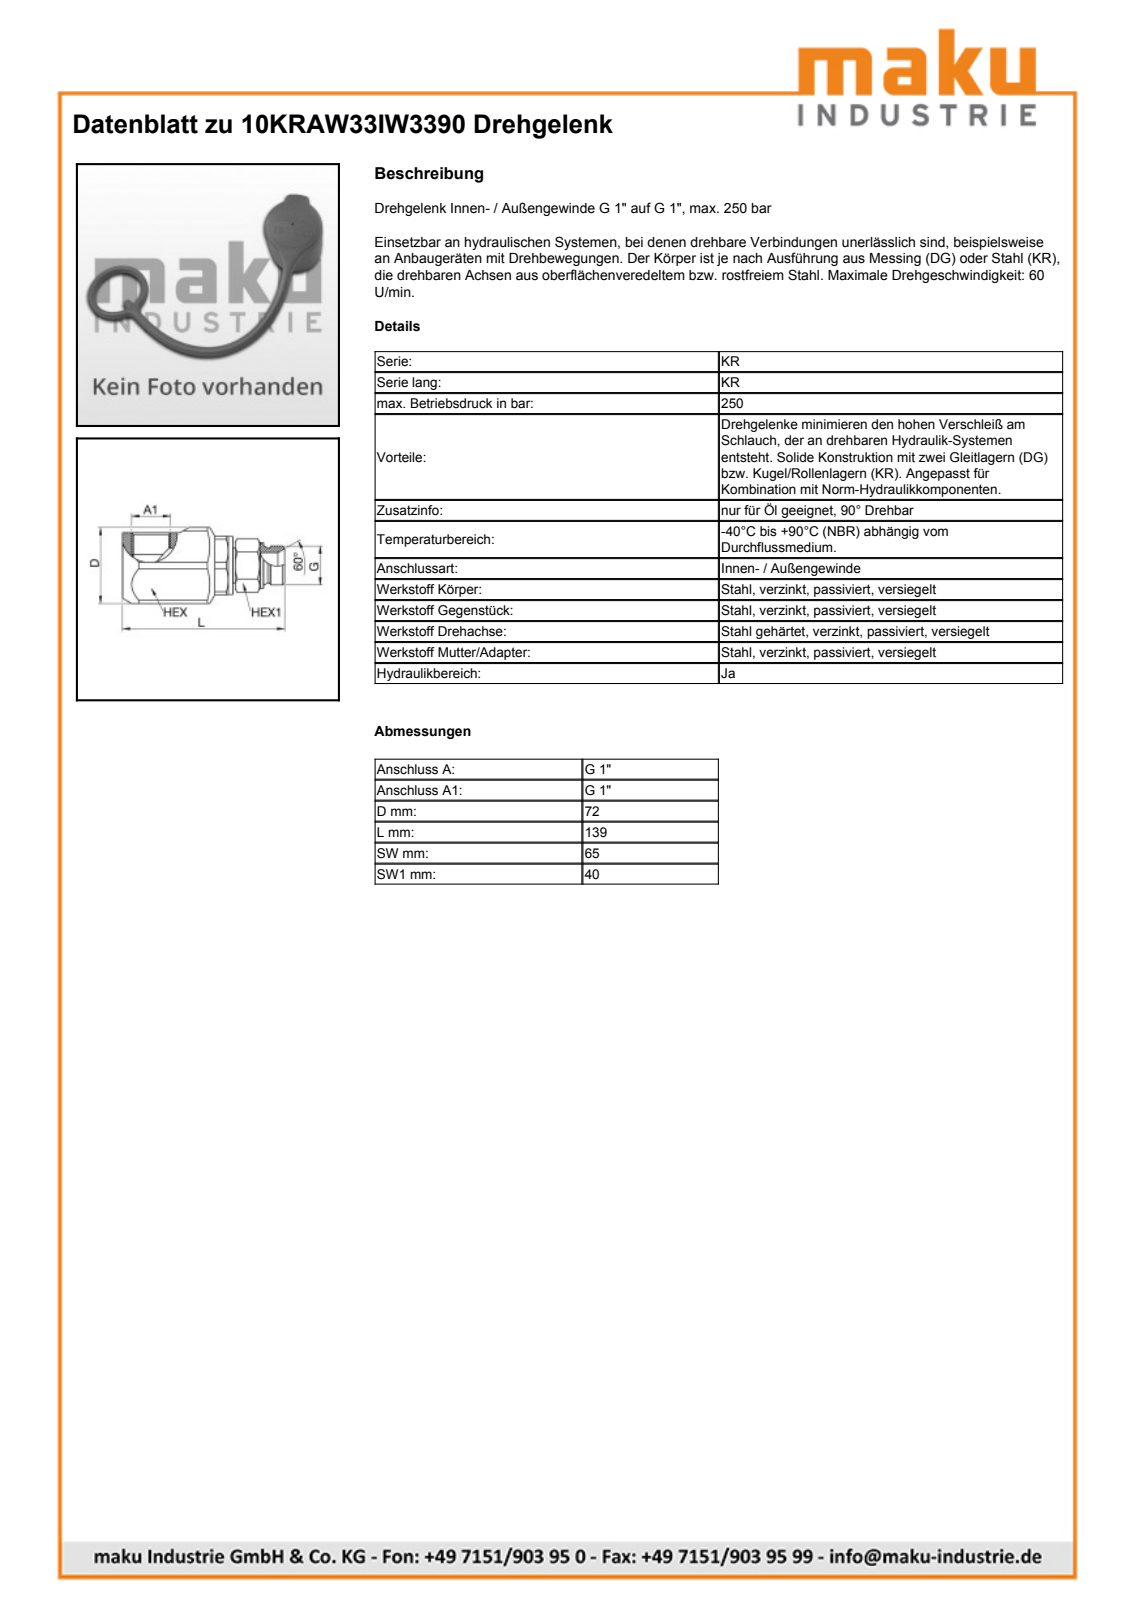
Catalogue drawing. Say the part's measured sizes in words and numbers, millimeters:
The part is named "10KRAW33IW3390". Its 3-D file was written by "SolidWorks 2009 (AUTOMOTIVE_DESIGN)". It is 1 solid with 162 faces: 34 planar, 39 cylindrical and 89 other. Overall it measures 138.5 by 72 by 65 millimeters. Its volume is 285 776 cubic millimeters and its surface area 43 087 square millimeters. Round holes: 1 of diameter 22, 1 of diameter 26, 1 of diameter 30.2, 1 of diameter 30.29, 1 of diameter 37. Round bosses or shafts: 1 of diameter 49.6, 1 of diameter 39, 1 of diameter 33.25, 1 of diameter 29.9, 1 of diameter 29. Partial cylindrical surfaces (rounded edges, fillets, slot ends): 1 of radius 22.5, 1 of radius 22.6, 1 of radius 27.5, 1 of radius 36. The main face-to-face distances are 65, 40, 7.5, 57.5, 60.5, 94.5, 4.5, 96.5, 2, 50.
